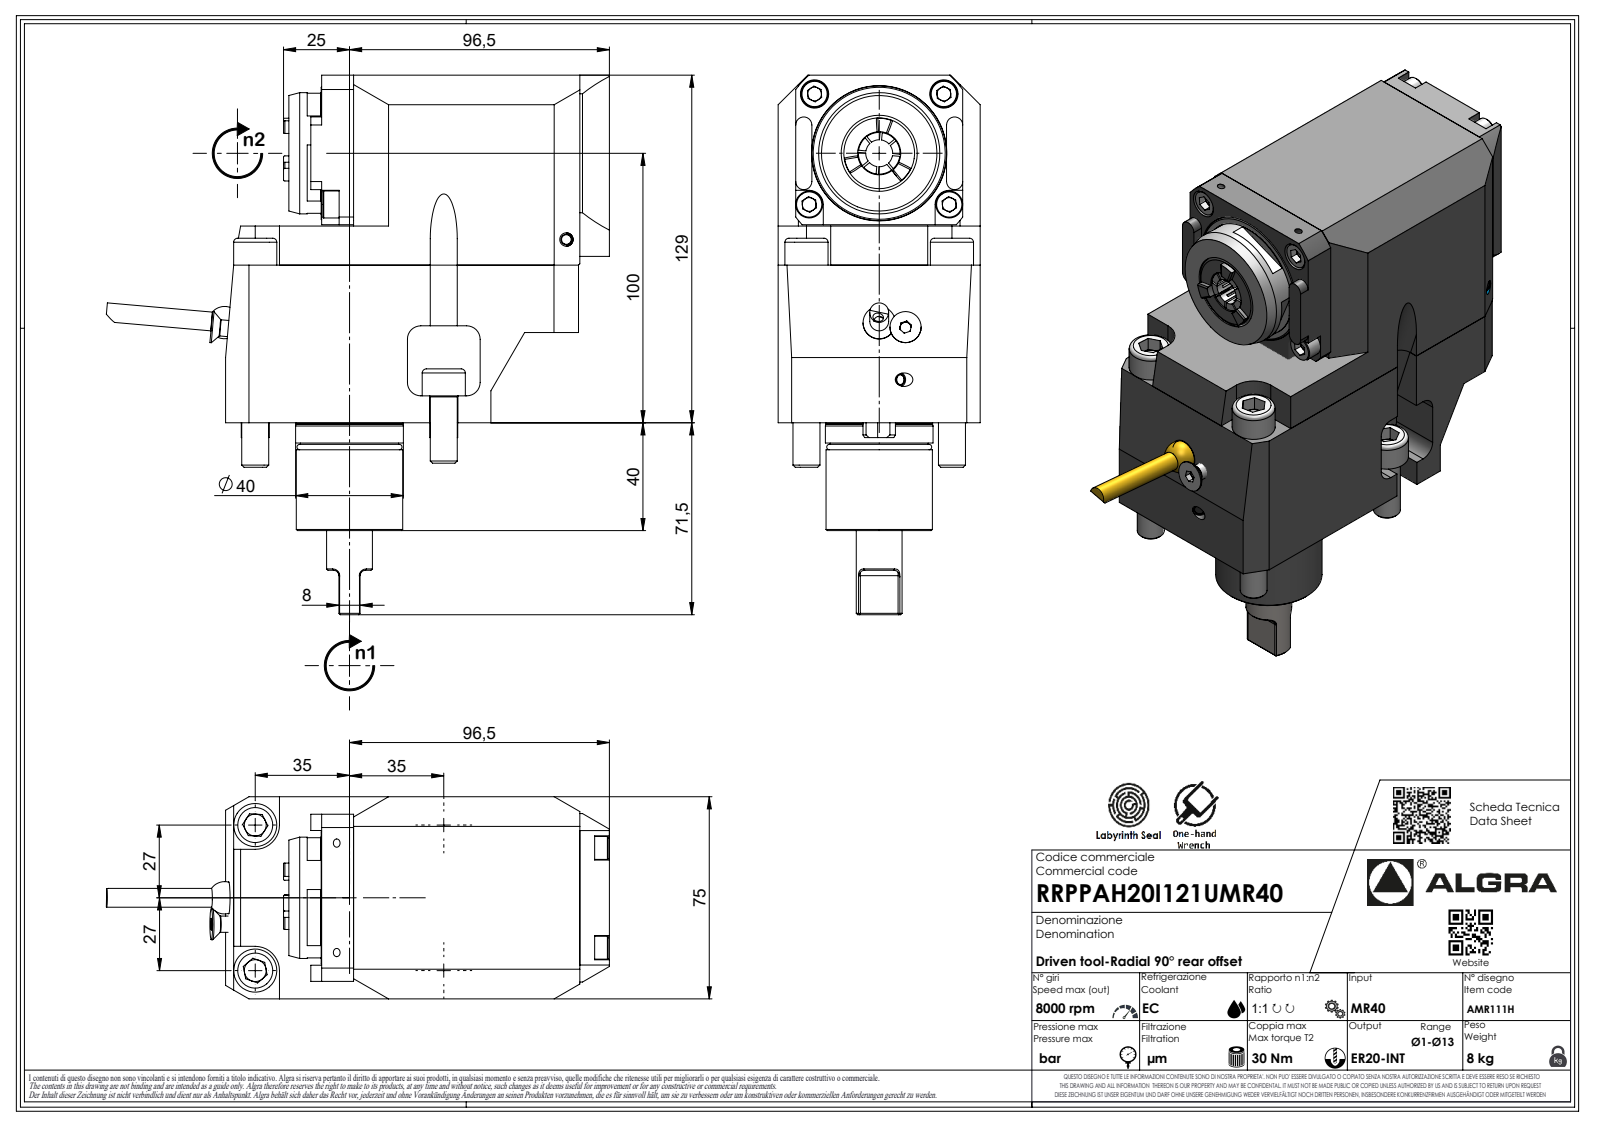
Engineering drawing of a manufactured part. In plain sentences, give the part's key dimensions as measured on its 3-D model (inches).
The part is named "RRPPAH20I121UMR40". Its 3-D file was written by "SolidWorks 2023 (AUTOMOTIVE_DESIGN)". It is 1 solid with 540 faces: 361 planar, 81 cylindrical and 98 other. Overall it measures 7.882 by 7.55 by 2.953 inches. Its volume is 69.02 cubic inches and its surface area 128.8 square inches. Round holes: 1 of diameter 0.083, 1 of diameter 0.157, 1 of diameter 0.197, 1 of diameter 0.337, 1 of diameter 0.472. Round bosses or shafts: 4 of diameter 0.394, 2 of diameter 0.63, 1 of diameter 1.772, 1 of diameter 1.575, 1 of diameter 1.559, 1 of diameter 1.555, 1 of diameter 1.474, 1 of diameter 0.669. Partial cylindrical surfaces (rounded edges, fillets, slot ends): 7 of radius 0.013, 7 of radius 0.02, 7 of radius 0.079, 7 of radius 0.146, 4 of radius 0.118, 2 of radius 0.128, 2 of radius 0.207, 2 of radius 0.236. The main face-to-face distances are 2.953, 5.079, 2.205, 2.874, 2.697, 0.453, 3.76, 2.894, 0.925, 1.575.
